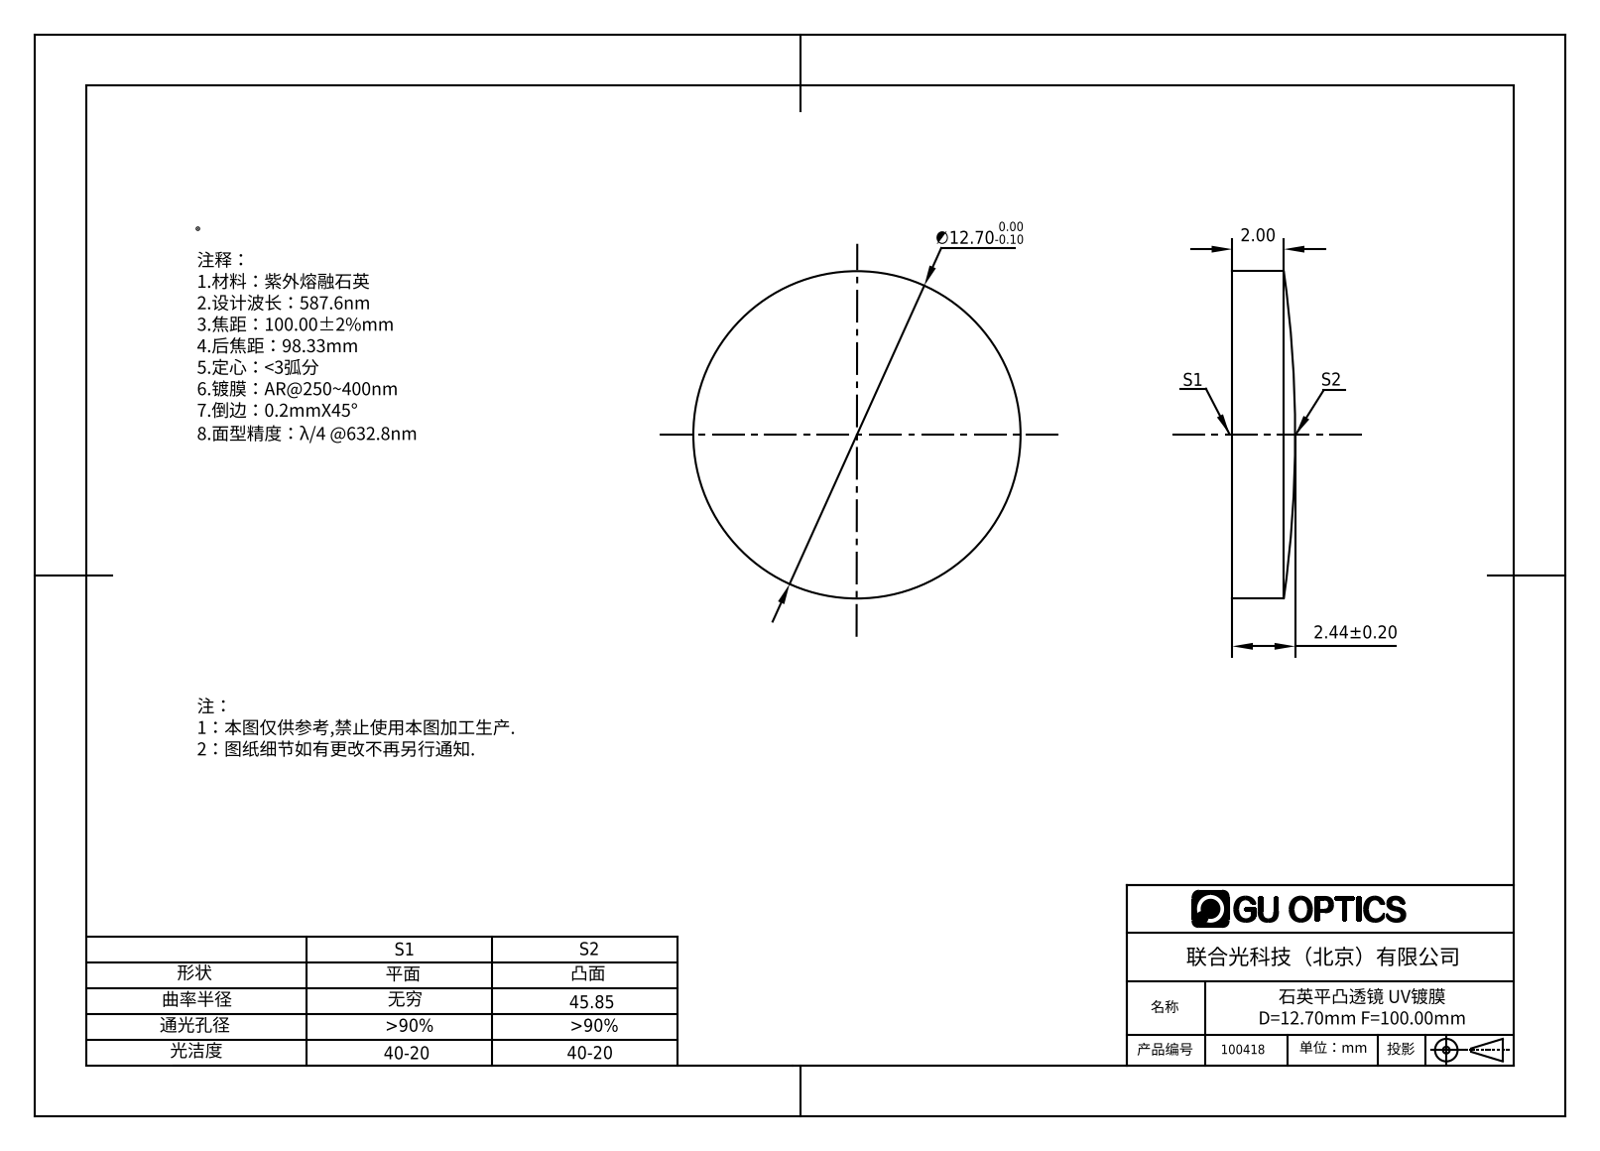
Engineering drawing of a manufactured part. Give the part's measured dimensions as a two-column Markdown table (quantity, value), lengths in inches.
| quantity | value |
| --- | --- |
| part name | 100368 |
| STEP written by | SolidWorks 2016 (AUTOMOTIVE_DESIGN) |
| units | inches |
| bodies | 1 solid, 5 faces (1 planar, 2 cylindrical, 2 other) |
| overall size | 0.5 × 0.5 × 0.096 |
| volume | 0.017 in³ |
| surface area | 0.518 in² |
| round bosses / shafts (diameter × count) | 0.5 × 1 |
